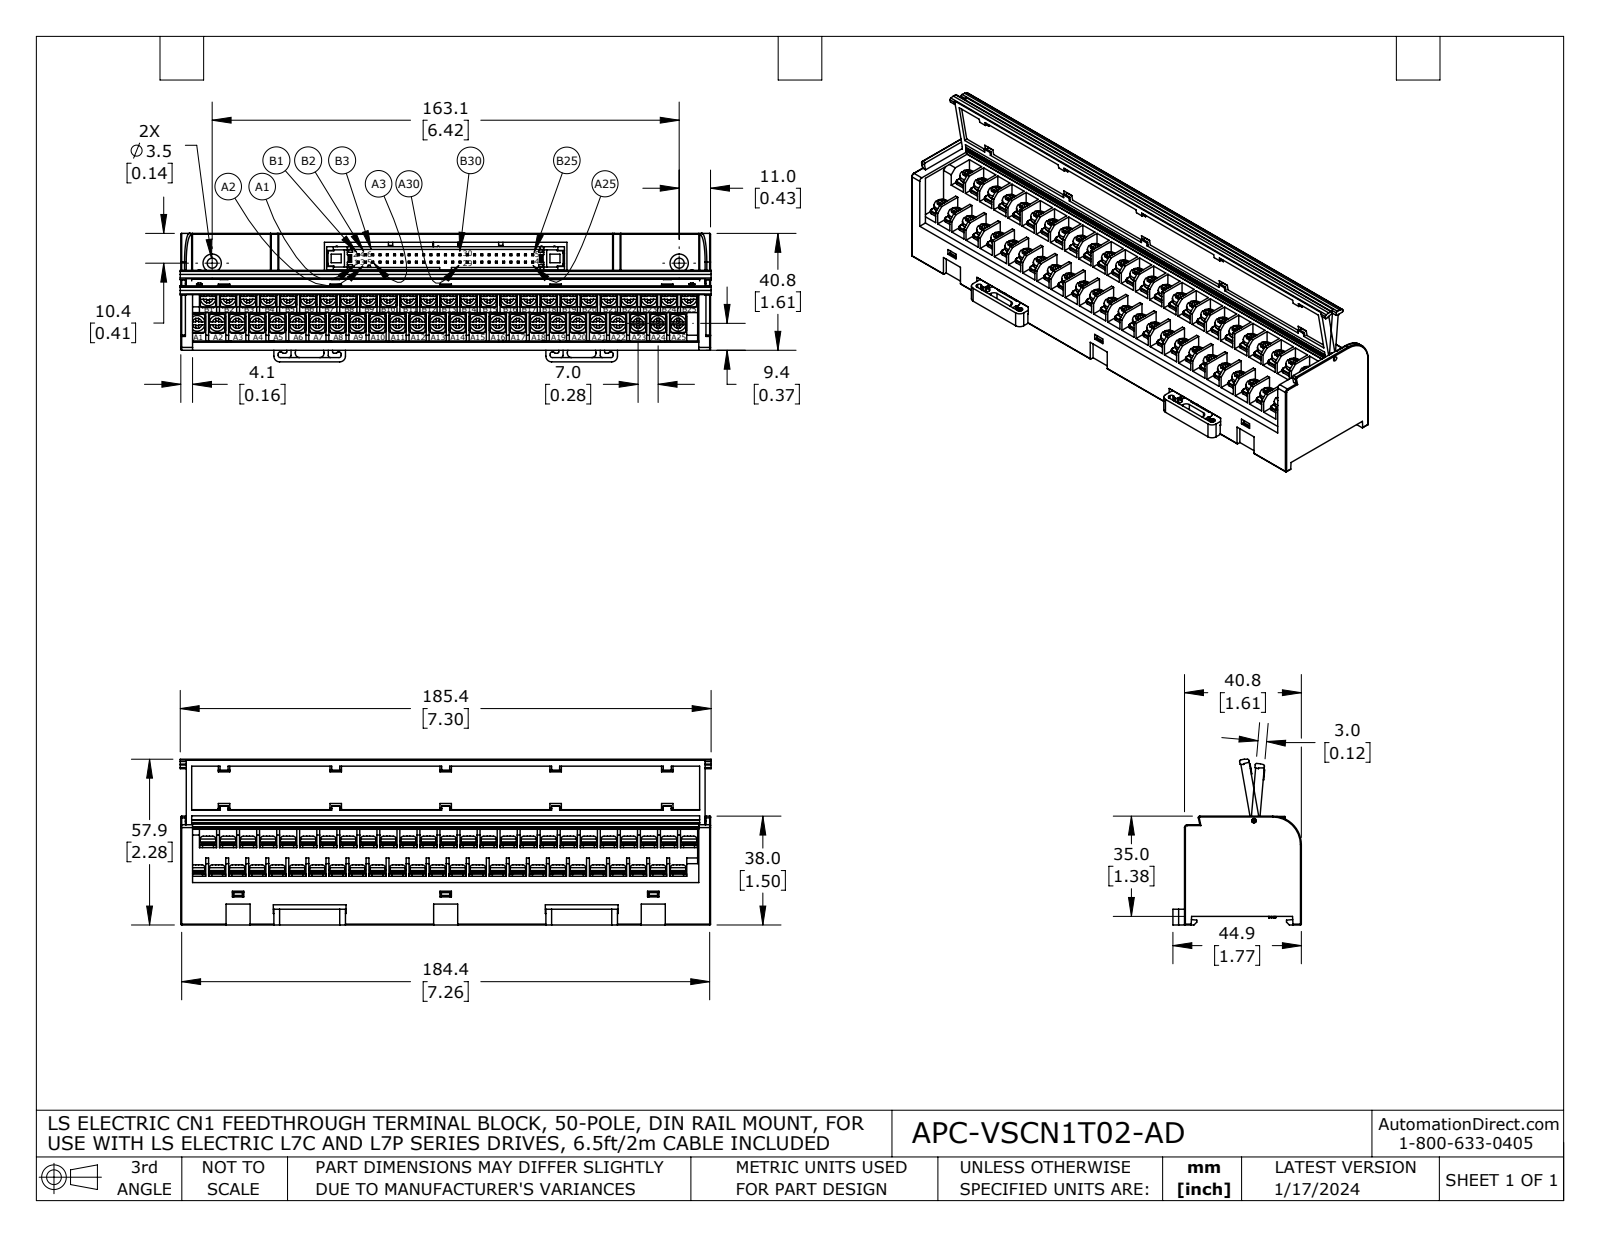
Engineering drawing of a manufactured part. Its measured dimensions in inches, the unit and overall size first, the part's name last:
Units: inches
Overall size (bounding box): 7.299 × 2.278 × 1.766
Round holes (diameter × count): ⌀0.087 ×50, ⌀0.059 ×2, ⌀0.098 ×2, ⌀0.1 ×2, ⌀0.138 ×2, ⌀0.252 ×2, ⌀0.061 ×1
Round bosses / shafts (diameter × count): ⌀0.217 ×50, ⌀0.079 ×50, ⌀0.28 ×2, ⌀0.276 ×2, ⌀0.197 ×2, ⌀0.059 ×2
Partial cylindrical surfaces — rounded edges, fillets, slot ends (radius × count): R0.039 ×209, R0.008 ×104, R0.012 ×36, R0.02 ×29, R0.03 ×20, R0.059 ×10, R0.024 ×4, R0.079 ×4
Main face-to-face distances: 0.071, 0.087, 0.018, 0.626, 0.089, 0.555, 0.644, 0.079, 0.039, 0.469
Hole centre spacings: 0.276, 0.551, 0.827, 1.102, 1.378, 1.654, 1.929, 2.205
Volume: 8.772 in³ · Surface area: 156.3 in²
Bodies: 4 solids, 4594 faces (3055 planar, 1004 cylindrical, 535 other)
Part name (STEP PRODUCT): APC-VSCN1T-AD
STEP written by: SolidWorks 2021 (AUTOMOTIVE_DESIGN)
